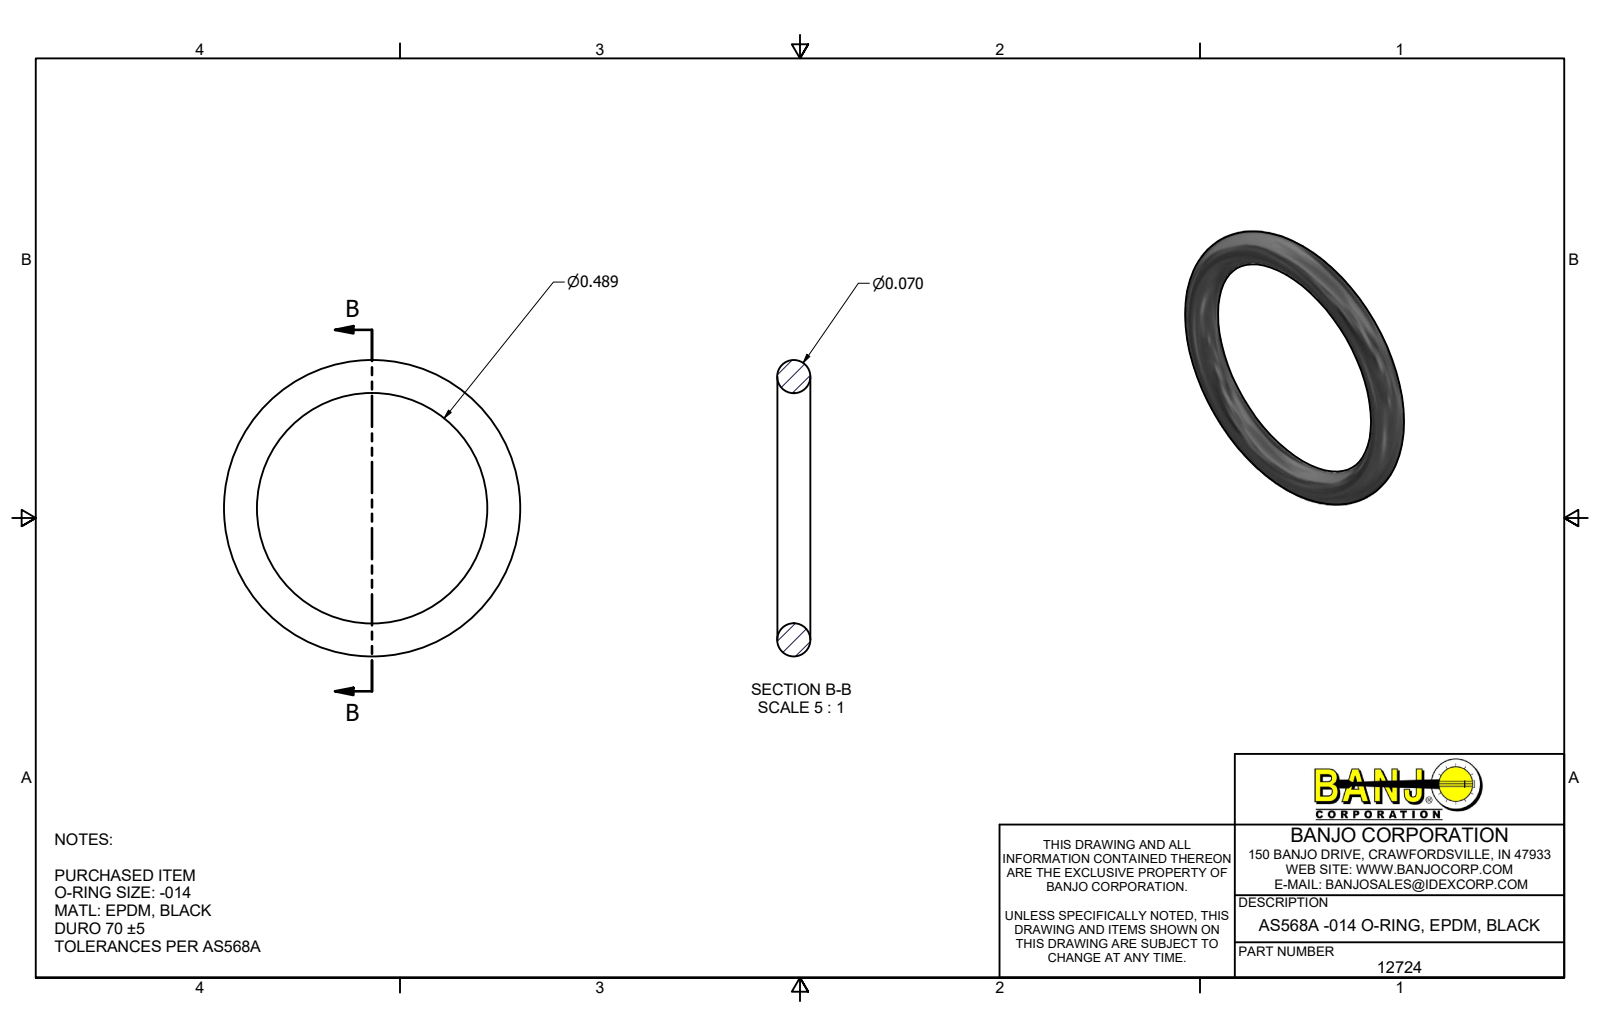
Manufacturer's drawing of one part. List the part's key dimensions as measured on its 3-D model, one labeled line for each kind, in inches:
Part name (STEP PRODUCT): 12724
STEP written by: Autodesk Inventor 2019 (AUTOMOTIVE_DESIGN)
Units: inches
Bodies: 1 solid, 1 faces (0 planar, 0 cylindrical, 1 other)
Overall size (bounding box): 0.629 × 0.629 × 0.07
Volume: 0.007 in³ · Surface area: 0.386 in²
